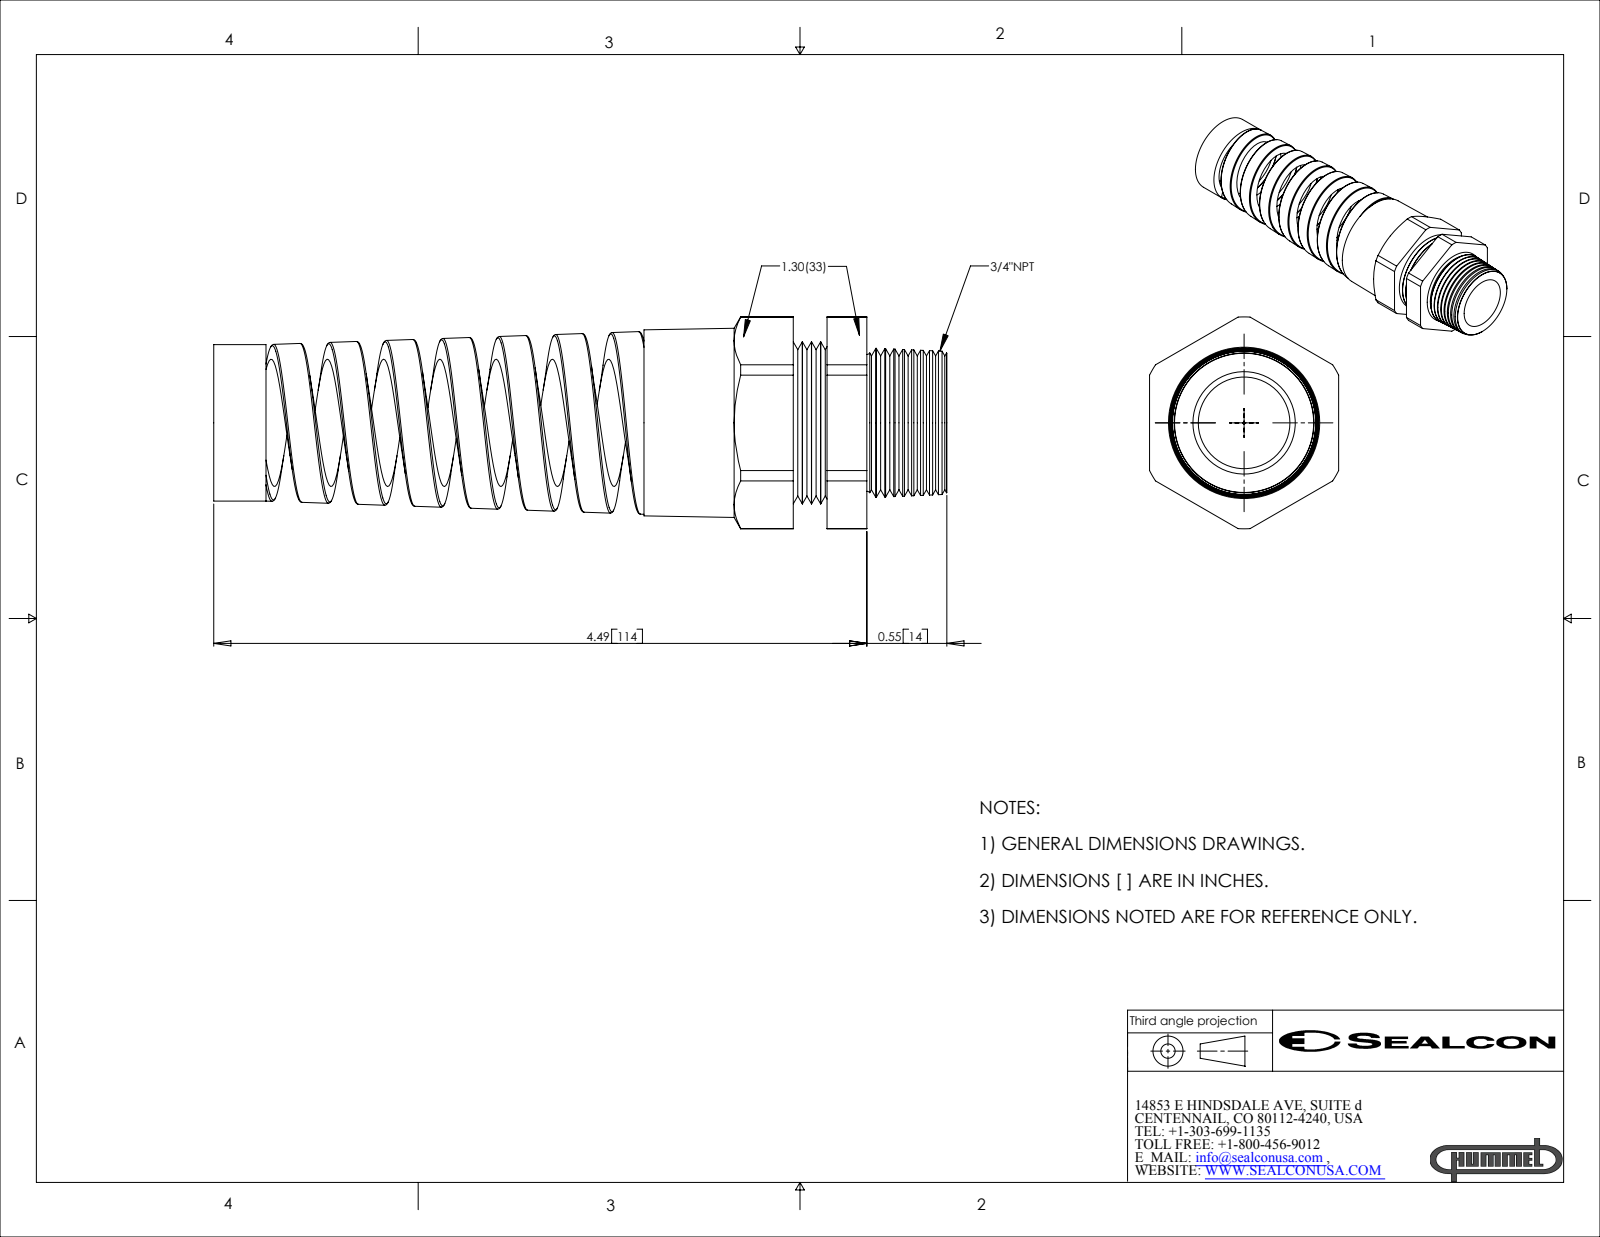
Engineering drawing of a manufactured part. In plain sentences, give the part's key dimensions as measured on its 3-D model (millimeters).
The part is named "CF21NR-GY". Its 3-D file was written by "SolidWorks 2007 (CONFIG_CONTROL_DESIGN)". It is 1 solid with 163 faces: 19 planar, 39 cylindrical and 105 other. Overall it measures 128 by 37 by 33 millimeters. Its volume is 40 620 cubic millimeters and its surface area 22 680 square millimeters. Round holes: 1 of diameter 16, 1 of diameter 22.2. Round bosses or shafts: 1 of diameter 28.3, 1 of diameter 27.3. Partial cylindrical surfaces (rounded edges, fillets, slot ends): 1 of radius 18.5. The main face-to-face distances are 33, 38.9, 26.1, 12.9, 32, 5.9, 7, 52.9, 26.8, 20.9.
